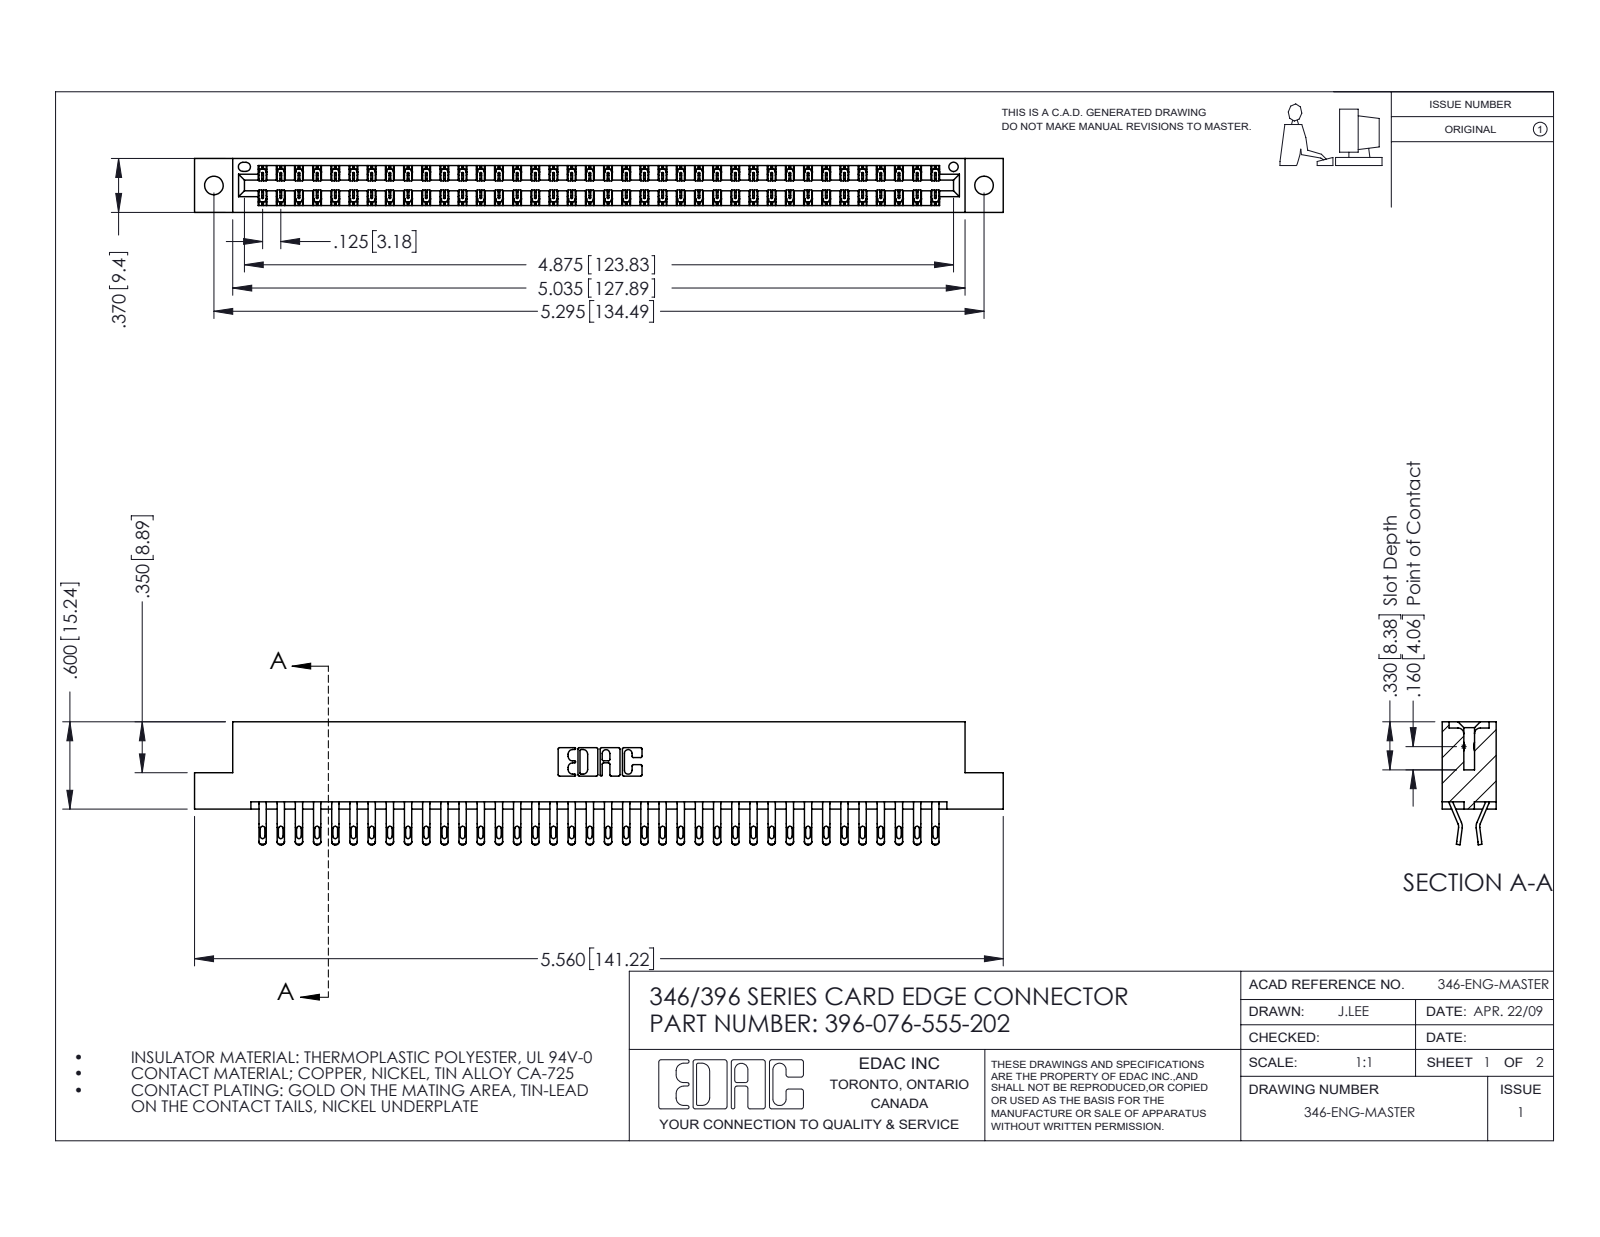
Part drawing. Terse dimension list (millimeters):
name: 396-076-555-202; 345-292-001_555 Tail; 346 Part_Flush Mounting Lugs - 0.128 Dia
written by: SolidWorks 2016 (CONFIG_CONTROL_DESIGN)
unit: mm
bodies: 77 solids, 4530 faces (2584 planar, 1946 cylindrical, 0 other)
size: 141.2 × 21.5 × 9.4
volume: 13 900 mm³; area: 19 590 mm²
holes: 2× ⌀3.3, 1× ⌀1.6
rounds: 152× R0.4, 152× R0.5, 114× R0.2, 22× R0.3, 6× R0.2, 6× R0.8, 3× R0.7, 2× R0.3
face distances: 1.2, 8.2, 9.4, 6.4, 0.6, 1.8, 7.6, 7, 3.8, 5.6
hole spacings: 6.2, 129.2, 134.5
